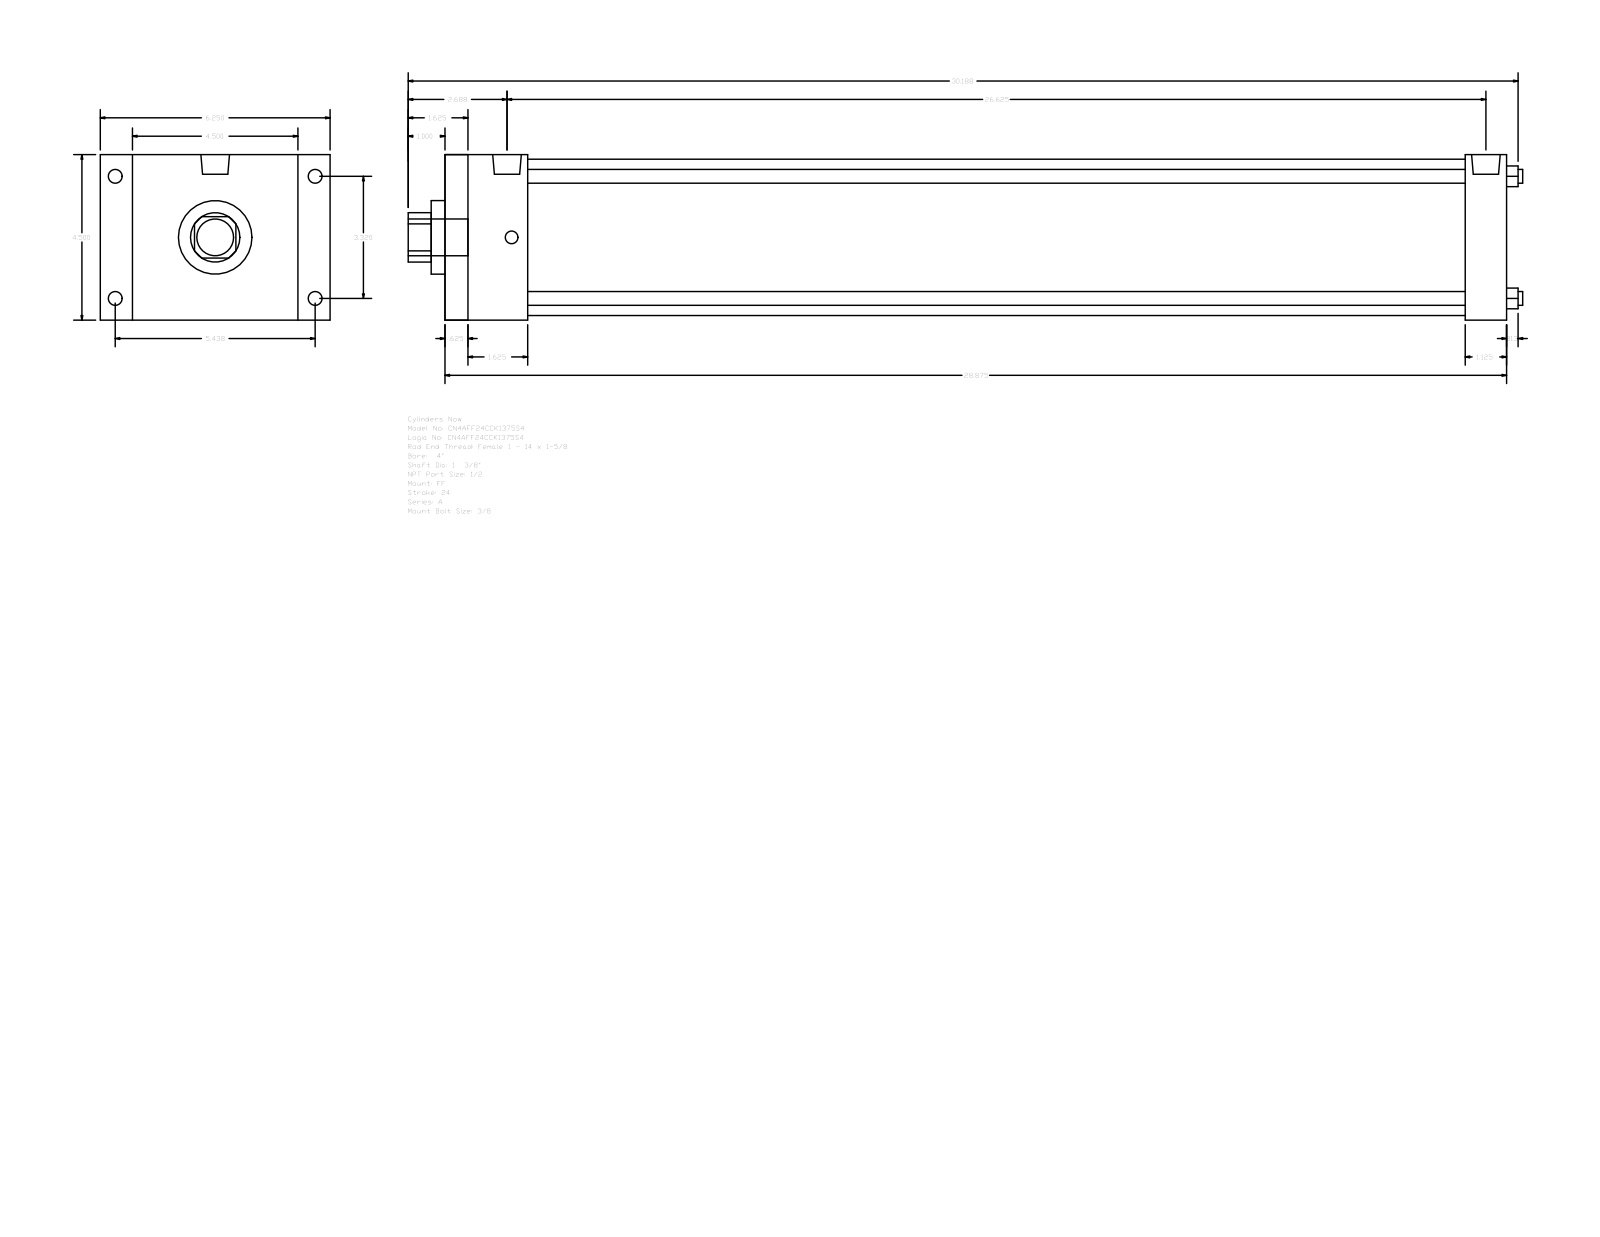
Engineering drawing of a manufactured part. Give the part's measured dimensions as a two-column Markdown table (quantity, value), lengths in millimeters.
| quantity | value |
| --- | --- |
| part name | A_FF__0400_1.375 |
| STEP written by | GSSL Pune (CONFIG_CONTROL_DESIGN) |
| units | millimeters |
| bodies | 0 solids, 92 faces (64 planar, 28 cylindrical, 0 other) |
| overall size | 769.94 × 158.75 × 114.3 |
| round holes (diameter × count) | 9.53 × 4, 34.92 × 1, 50.8 × 1, 107.95 × 1 |
| round bosses / shafts (diameter × count) | 9.53 × 4, 8.73 × 4, 19.77 × 2, 25.4 × 1 |
| partial cylindrical surfaces (radius × count) | 17.06 × 1 |
| main face-to-face distances | 114.3, 733.43, 15.87, 717.56, 28.58, 22.23, 136.53, 704.85, 688.98, 57.15 |
| hole center spacings | 59.62, 84.32, 119.25 |
